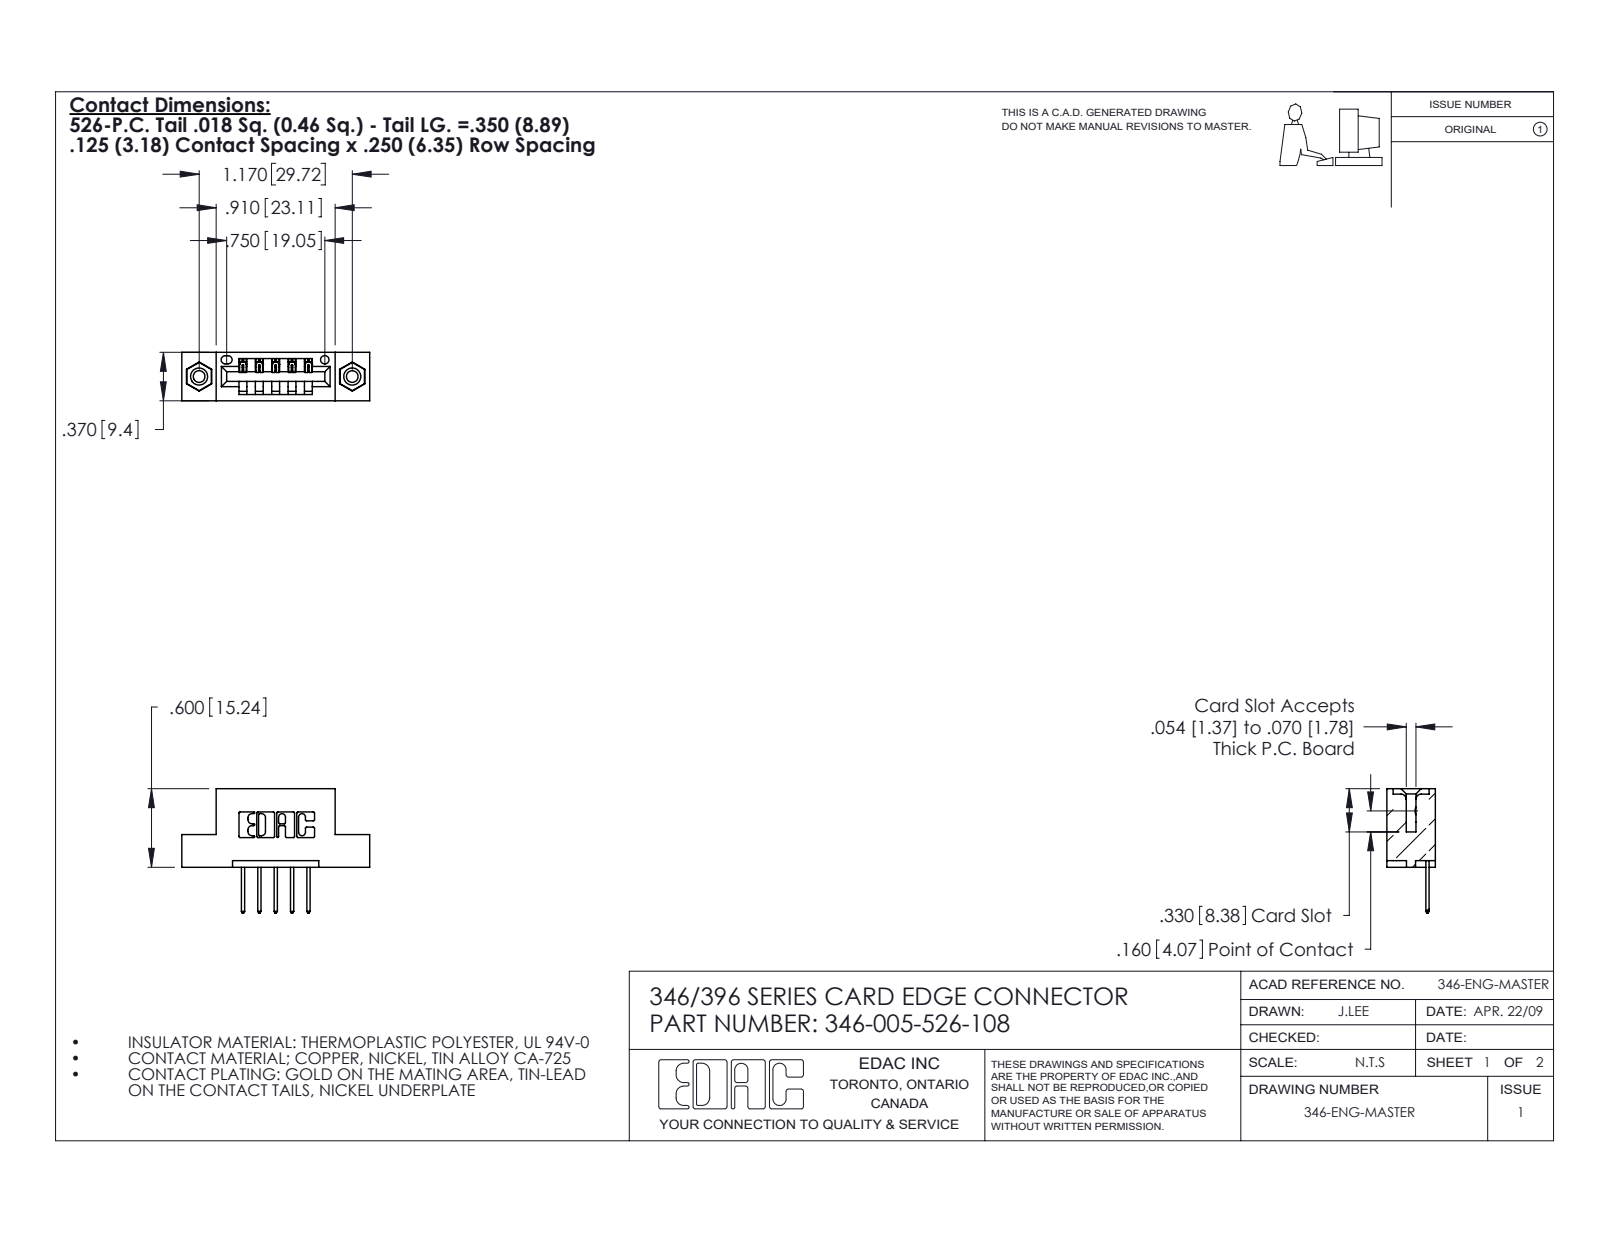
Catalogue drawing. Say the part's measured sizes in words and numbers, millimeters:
The part is named "346-005-526-108; 346 Part_Flush Mounting Lugs - 0.156 Dia-TI; 345-250-001_345-250-003-102; 345-292-001_345-293-126". Its 3-D file was written by "SolidWorks 2020 (CONFIG_CONTROL_DESIGN)". It is 8 solids with 472 faces: 308 planar, 148 cylindrical and 16 other. Overall it measures 36.4 by 24.1 by 9.4 millimeters. Its volume is 3 230 cubic millimeters and its surface area 3 646 square millimeters. Round holes: 2 of diameter 2.3, 2 of diameter 3.2, 2 of diameter 4, 1 of diameter 1.6. Round bosses or shafts: 2 of diameter 3.9. Partial cylindrical surfaces (rounded edges, fillets, slot ends): 22 of radius 0.3, 10 of radius 0.2, 10 of radius 0.3, 6 of radius 0.2, 6 of radius 0.8, 3 of radius 0.7, 2 of radius 0.8, 2 of radius 1. The main face-to-face distances are 6.4, 9.4, 1.2, 8.2, 14, 3.8, 5.6, 2.5, 4.4, 3.2. The hole center spacings are 6.2, 24.6, 29.7.
